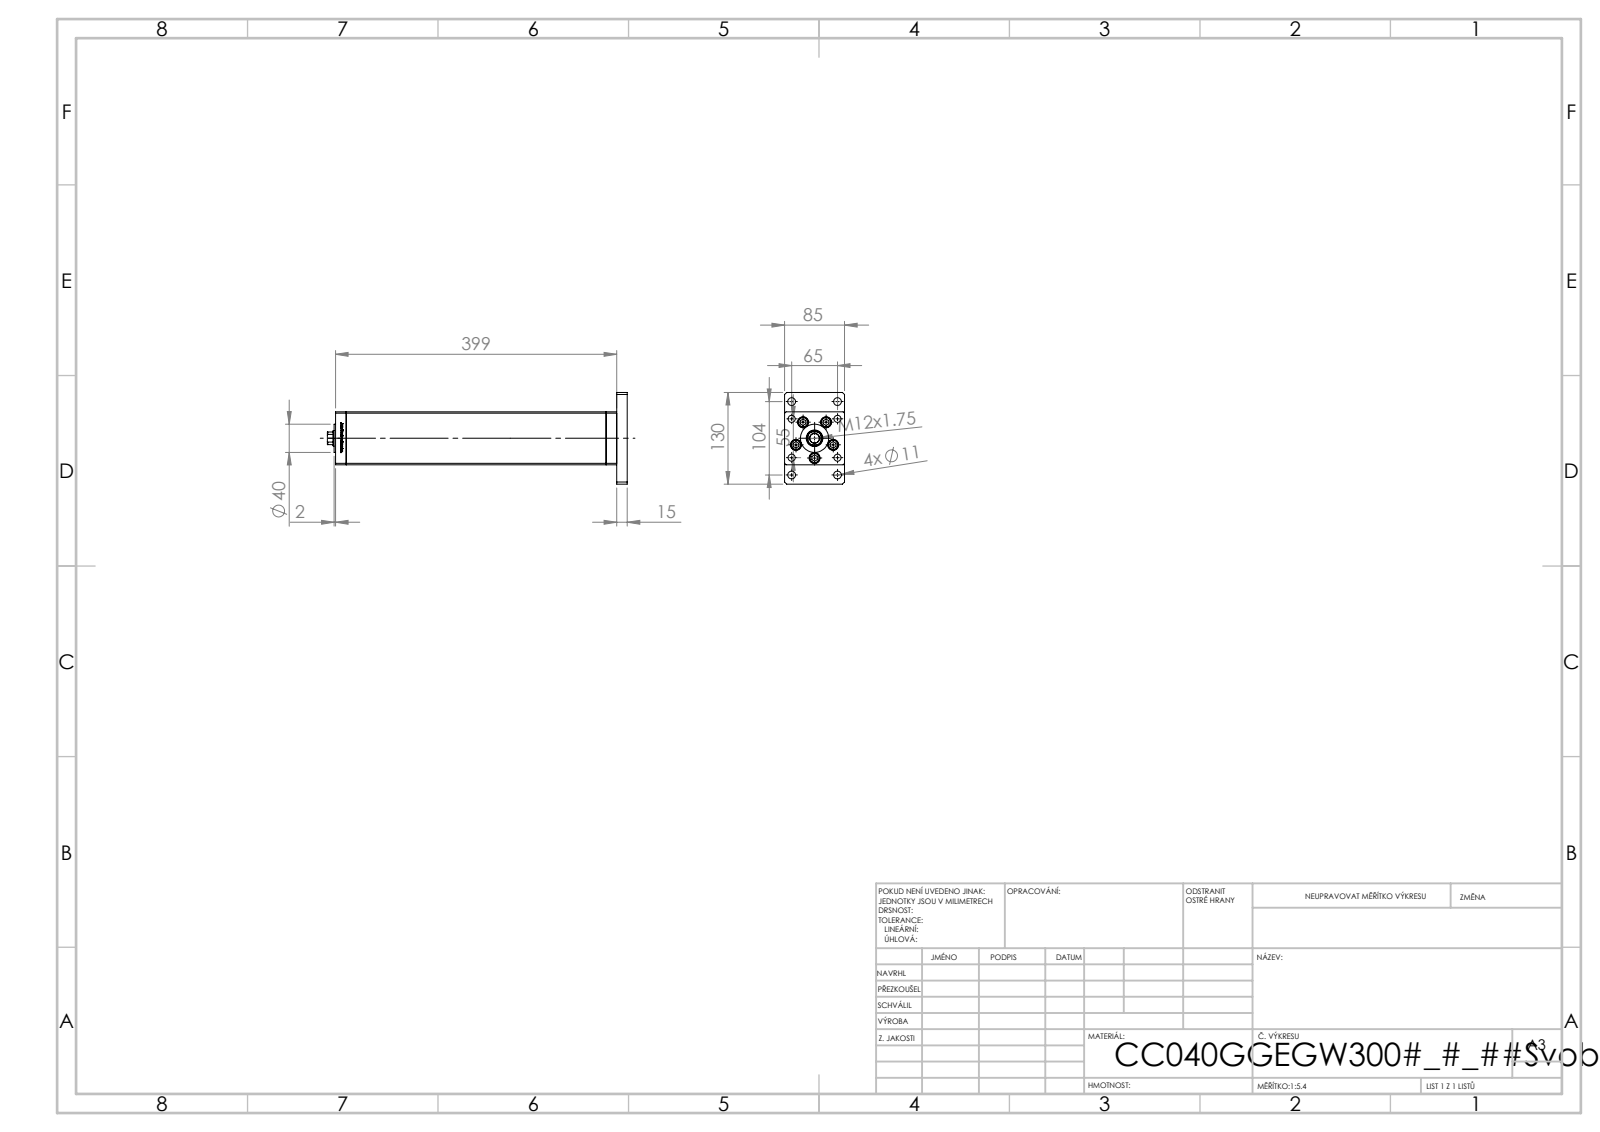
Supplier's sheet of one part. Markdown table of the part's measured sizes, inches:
| quantity | value |
| --- | --- |
| part name | V220C_F; V220C_G_MIDDLE; V220C BACK_G; V220C_FRONT_G (+2 more) |
| STEP written by | SolidWorks 2019 (CONFIG_CONTROL_DESIGN) |
| units | inches |
| bodies | 19 solids, 1313 faces (518 planar, 189 cylindrical, 606 other) |
| overall size | 16.732 × 5.118 × 3.346 |
| volume | 141.8 in³ |
| surface area | 488.5 in² |
| round holes (diameter × count) | 0.394 × 9, 0.433 × 9, 0.61 × 5, 0.571 × 4, 0.079 × 2, 0.518 × 2, 0.531 × 1, 0.866 × 1, 0.925 × 1, 2.205 × 1 |
| round bosses / shafts (diameter × count) | 0.315 × 9, 0.571 × 5, 1.575 × 1 |
| partial cylindrical surfaces (radius × count) | 0.037 × 2, 0.413 × 1 |
| main face-to-face distances | 3.346, 2.953, 0.591, 15.098, 15.689, 14.508, 1.181, 2.539, 0.413, 0.079 |
| hole center spacings | 1.102, 0.965, 1.676, 2.414, 2.559, 2.735, 3.13, 4.043 |
